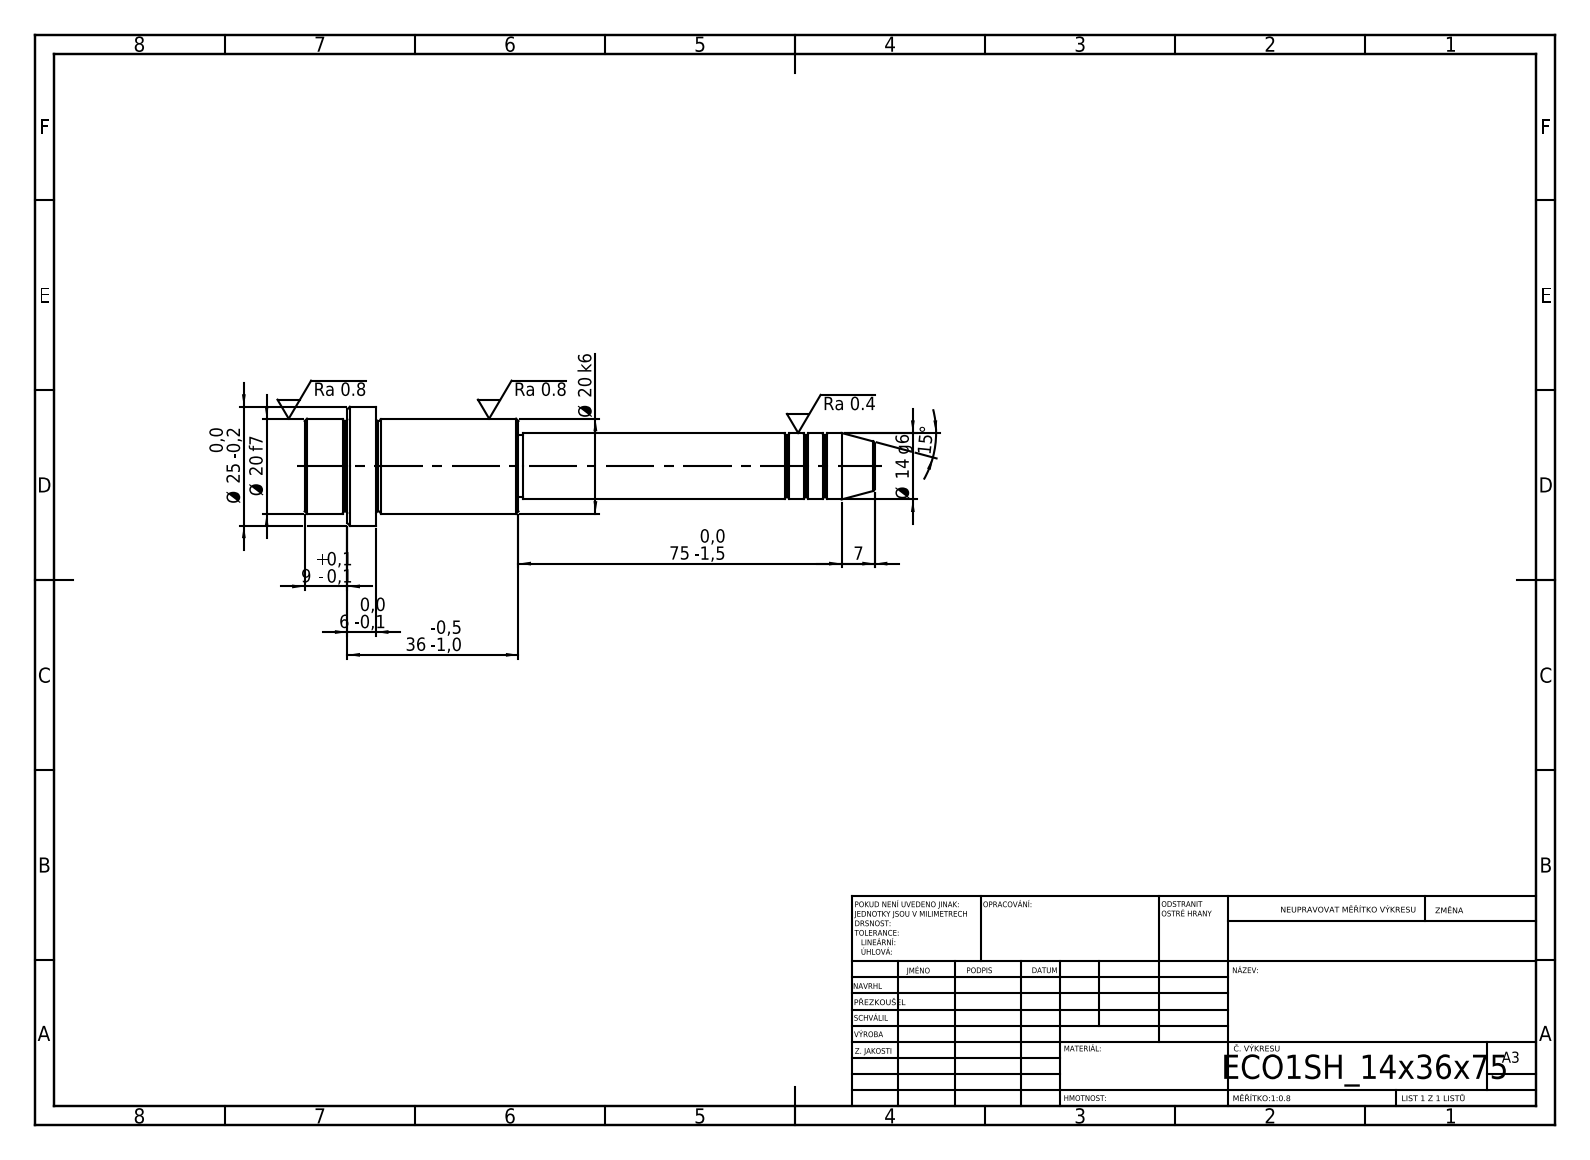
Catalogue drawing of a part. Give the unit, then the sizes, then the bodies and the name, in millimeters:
Units: millimetres
Overall size (bounding box): 120 × 25 × 25
Round bosses / shafts (diameter × count): ⌀25 ×1, ⌀20 ×1, ⌀14 ×1, ⌀13 ×1
Main face-to-face distances: 15, 30, 45, 36, 6, 9, 75, 105, 111, 120
Volume: 26 334 mm³ · Surface area: 7 205 mm²
Bodies: 1 solid, 52 faces (6 planar, 16 cylindrical, 30 other)
STEP written by: SolidWorks 2019 (CONFIG_CONTROL_DESIGN)
